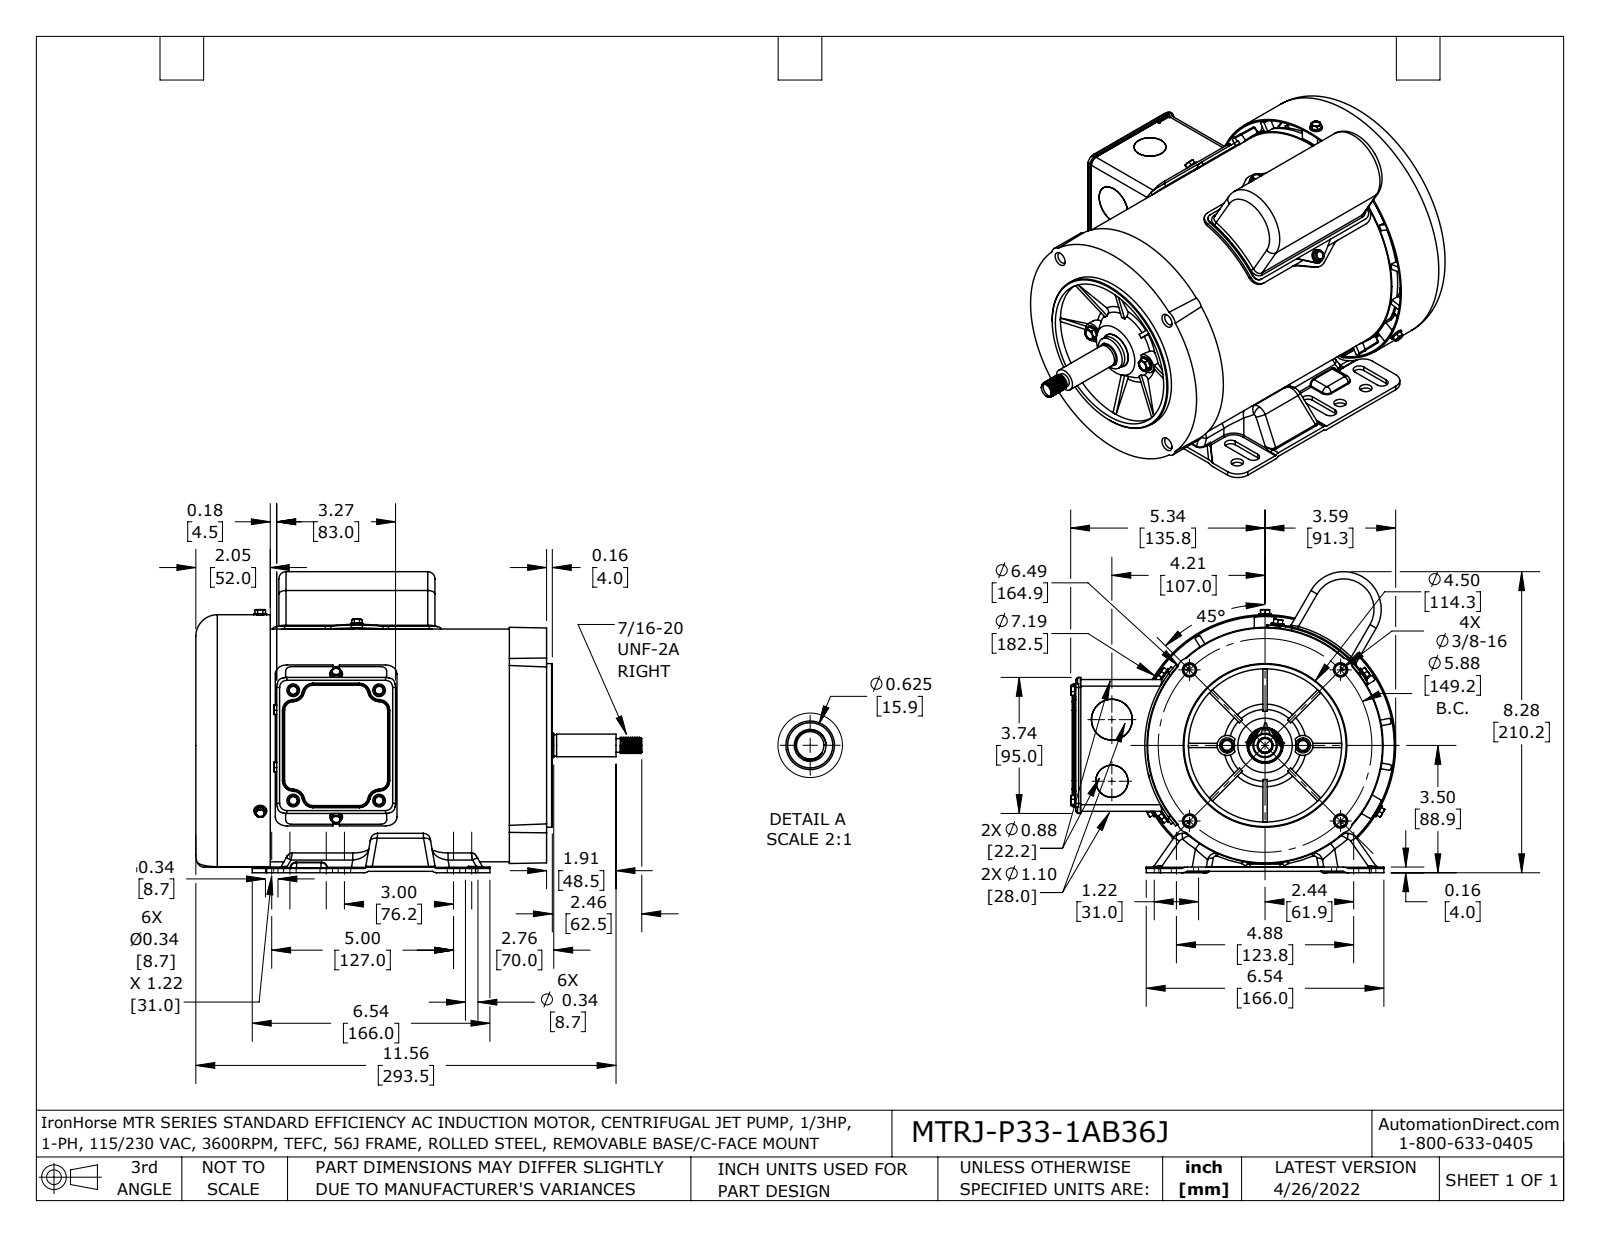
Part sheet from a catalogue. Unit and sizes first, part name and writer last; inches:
Units: inches
Overall size (bounding box): 12.264 × 8.938 × 8.276
Round holes (diameter × count): ⌀0.219 ×13, ⌀0.197 ×12, ⌀0.276 ×8, ⌀0.177 ×6, ⌀0.217 ×6, ⌀0.328 ×6, ⌀0.344 ×6, ⌀0.136 ×5, ⌀0.15 ×4, ⌀0.313 ×4, ⌀0.709 ×3, ⌀0.13 ×2
Round bosses / shafts (diameter × count): ⌀0.164 ×13, ⌀0.348 ×10, ⌀0.236 ×6, ⌀0.348 ×3, ⌀0.414 ×2, ⌀0.19 ×2, ⌀7.185 ×1, ⌀6.398 ×1
Partial cylindrical surfaces — rounded edges, fillets, slot ends (radius × count): R0.118 ×113, R0.039 ×57, R0.157 ×32, R0.02 ×30, R0.138 ×26, R0.197 ×20, R0.079 ×18, R0.276 ×18
Main face-to-face distances: 0.039, 0.118, 0.063, 0.031, 9.646, 9.606, 0.157, 3.559, 0.079, 3.087
Hole centre spacings: 4.221, 3.031, 0.094, 2.32, 2.409, 2.937, 3.748, 3.841
Volume: 47.59 in³ · Surface area: 982.9 in²
Bodies: 34 solids, 2940 faces (731 planar, 966 cylindrical, 1243 other)
Part name (STEP PRODUCT): MTRJ-P33-1AB36J redcmb1 coord
STEP written by: SolidWorks 2021 (AUTOMOTIVE_DESIGN)
